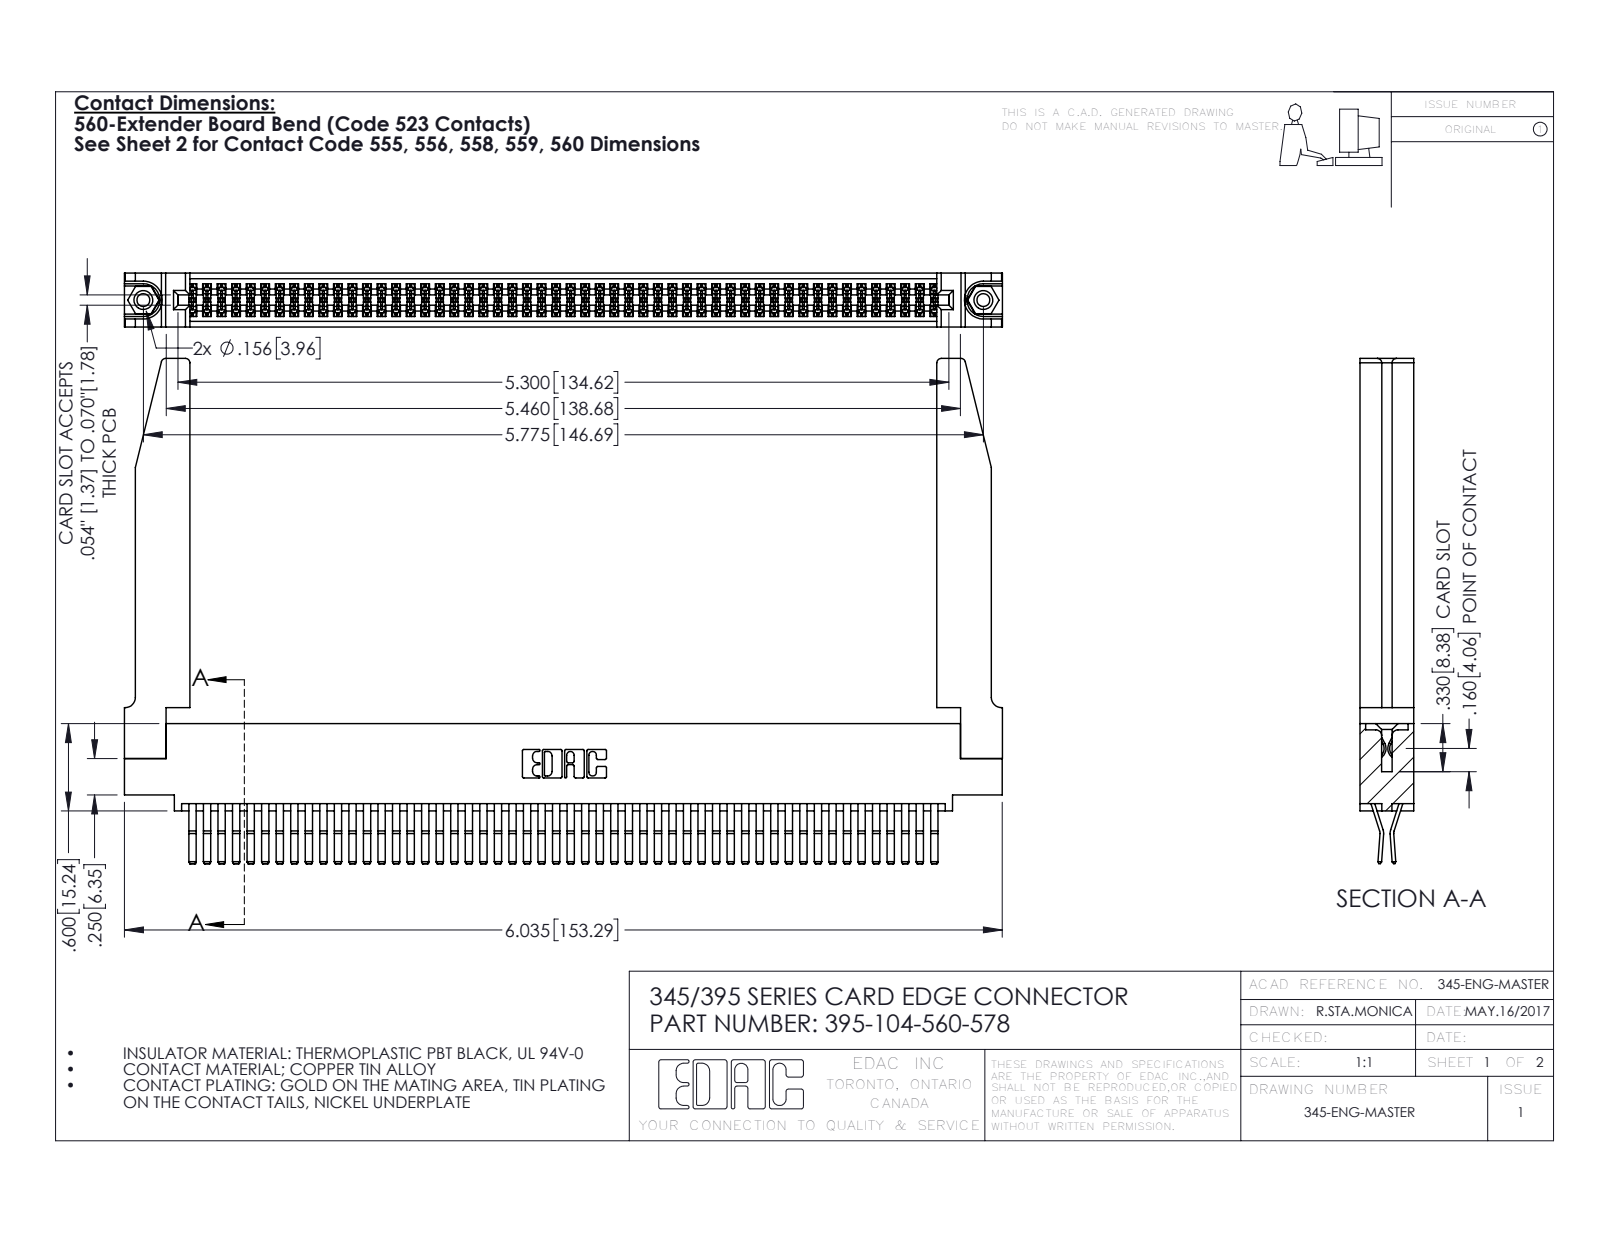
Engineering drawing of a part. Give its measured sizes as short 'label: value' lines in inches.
name: 345-292-001_560 Tail; 345-250-001_345-250-001-102; 345 Part_0.110 Offset - 0.156 Dia-TH; 395-104-560-578 (+1 more)
written by: SolidWorks 2016 (CONFIG_CONTROL_DESIGN)
unit: in
bodies: 109 solids, 5772 faces (3658 planar, 2062 cylindrical, 52 other)
size: 6.036 × 3.472 × 0.37
volume: 1.426 in³; area: 49.49 in²
holes: 2× ⌀0.089, 2× ⌀0.125, 2× ⌀0.156, 1× ⌀0.064
bosses: 2× ⌀0.155
rounds: 157× R0.006, 22× R0.01, 8× R0.03, 6× R0.007, 6× R0.031, 3× R0.026, 2× R0.01, 2× R0.014
face distances: 0.072, 0.37, 0.298, 0.025, 0.098, 0.272, 0.2, 0.225, 0.175, 0.15
hole spacings: 0.27, 5.539, 5.775
